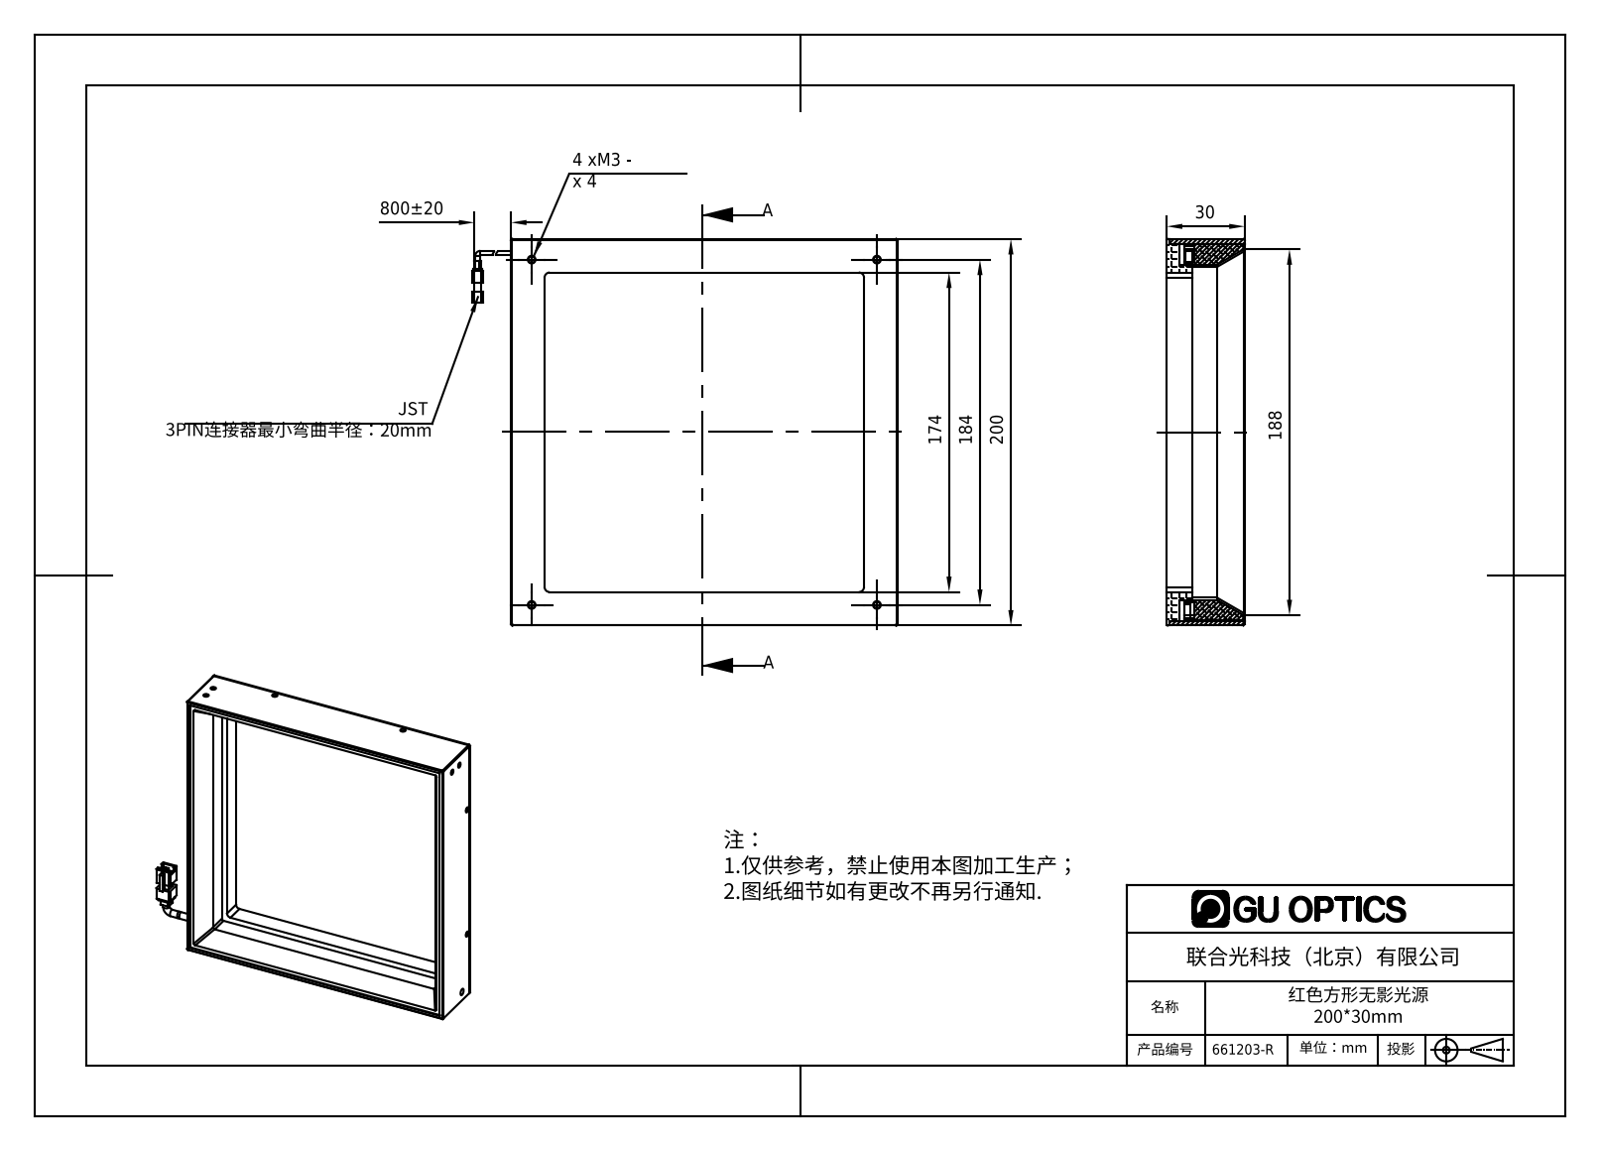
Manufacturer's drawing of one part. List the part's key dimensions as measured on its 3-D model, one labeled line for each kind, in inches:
Part name (STEP PRODUCT): 661203-R
STEP written by: SolidWorks 2016 (AUTOMOTIVE_DESIGN)
Units: inches
Bodies: 5 solids, 512 faces (228 planar, 183 cylindrical, 101 other)
Overall size (bounding box): 6.969 × 5.906 × 1.189
Volume: 8.649 in³ · Surface area: 154.2 in²
Round holes (diameter × count): ⌀0.049 ×12, ⌀0.059 ×12, ⌀0.063 ×12, ⌀0.11 ×12, ⌀0.098 ×4, ⌀0.118 ×4
Round bosses / shafts (diameter × count): ⌀0.138 ×2
Partial cylindrical surfaces — rounded edges, fillets, slot ends (radius × count): R0.039 ×15, R0.02 ×8, R0.079 ×4
Main face-to-face distances: 0.071, 5.835, 0.079, 5.827, 5.756, 5.764, 5.437, 5.906, 5.748, 0.39
Hole centre spacings: 0.315, 1.285, 1.4, 4.206, 4.243, 5.276, 5.433, 5.442
